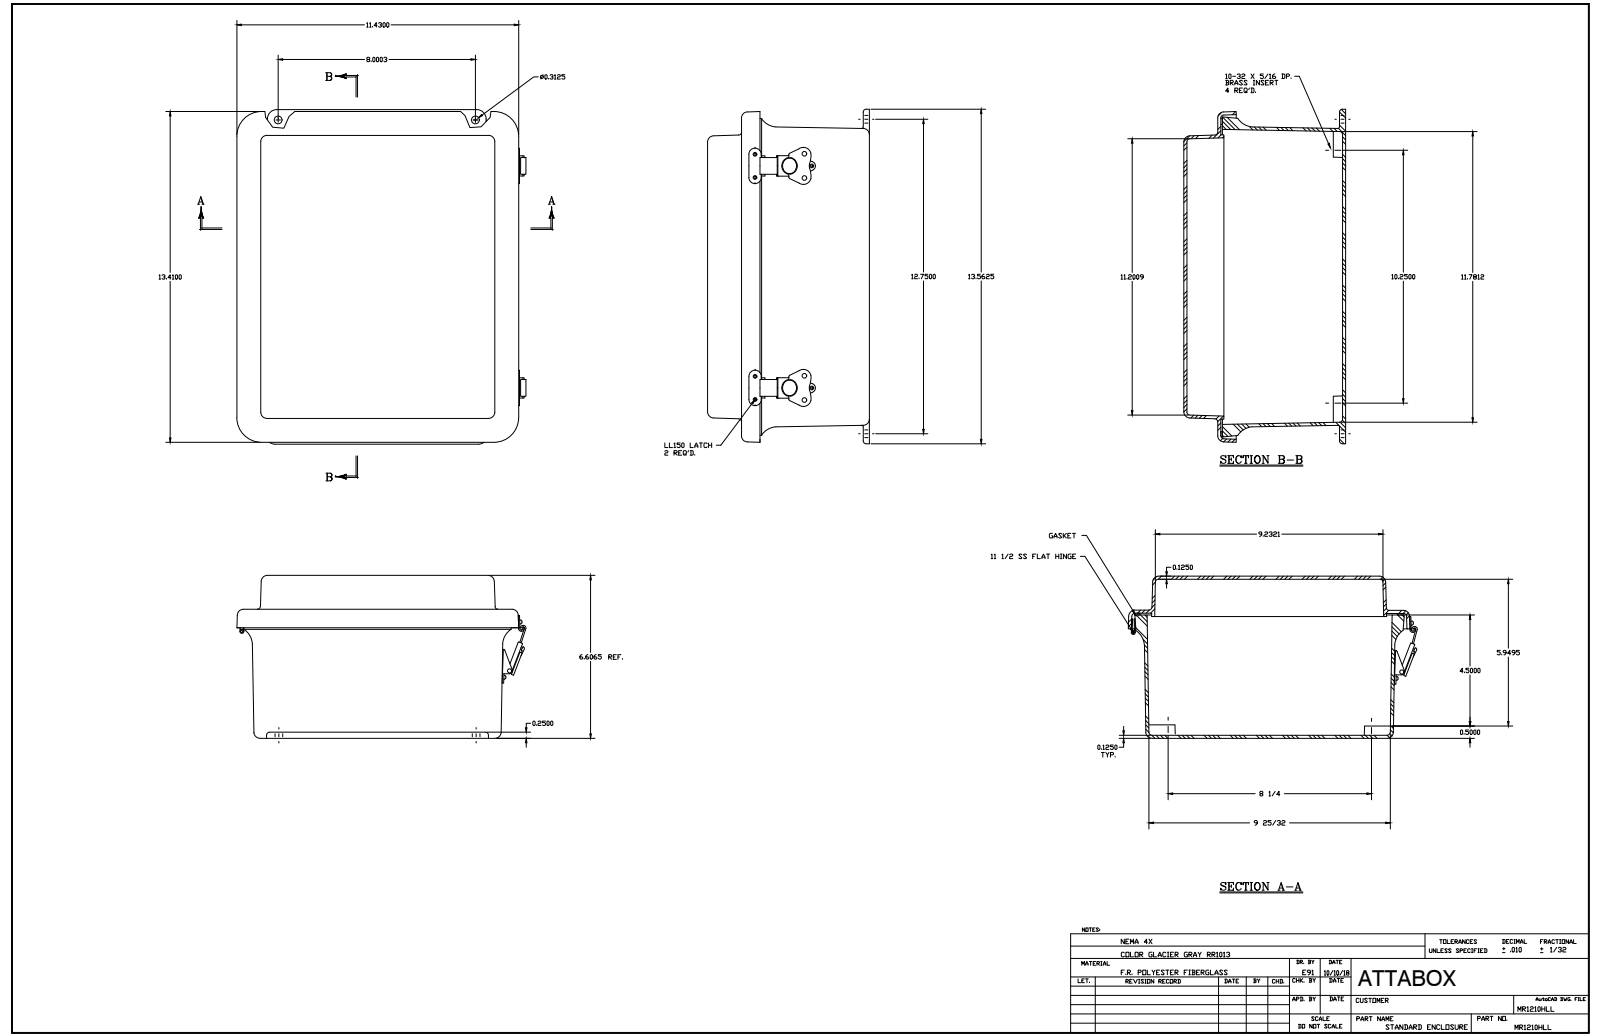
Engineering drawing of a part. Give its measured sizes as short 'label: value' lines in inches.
name: MR1210HLL
written by: SolidWorks 2018 (AUTOMOTIVE_DESIGN)
unit: in
bodies: 48 solids, 1208 faces (532 planar, 461 cylindrical, 215 other)
size: 13.563 × 11.61 × 6.588
volume: 92.16 in³; area: 1 306 in²
holes: 16× ⌀0.14, 8× ⌀0.131, 5× ⌀0.152, 4× ⌀0.13, 4× ⌀0.156, 4× ⌀0.165, 4× ⌀0.197, 4× ⌀0.218, 2× ⌀0.118, 2× ⌀0.138, 2× ⌀0.181, 2× ⌀0.182
bosses: 16× ⌀0.25, 9× ⌀0.125, 7× ⌀0.125, 4× ⌀0.27, 2× ⌀0.583, 2× ⌀0.524, 2× ⌀0.209, 2× ⌀0.185
rounds: 20× R0.031, 20× R0.125, 19× R0.079, 12× R0.25, 8× R0.037, 8× R0.039, 8× R0.045, 8× R0.047
face distances: 0.125, 6.463, 6.588, 6.337, 5.076, 1.387, 4.95, 1.512, 5.201, 1.262
hole spacings: 9, 3.625, 0.7, 0.938, 1.348, 1.465, 2.189, 9.031
